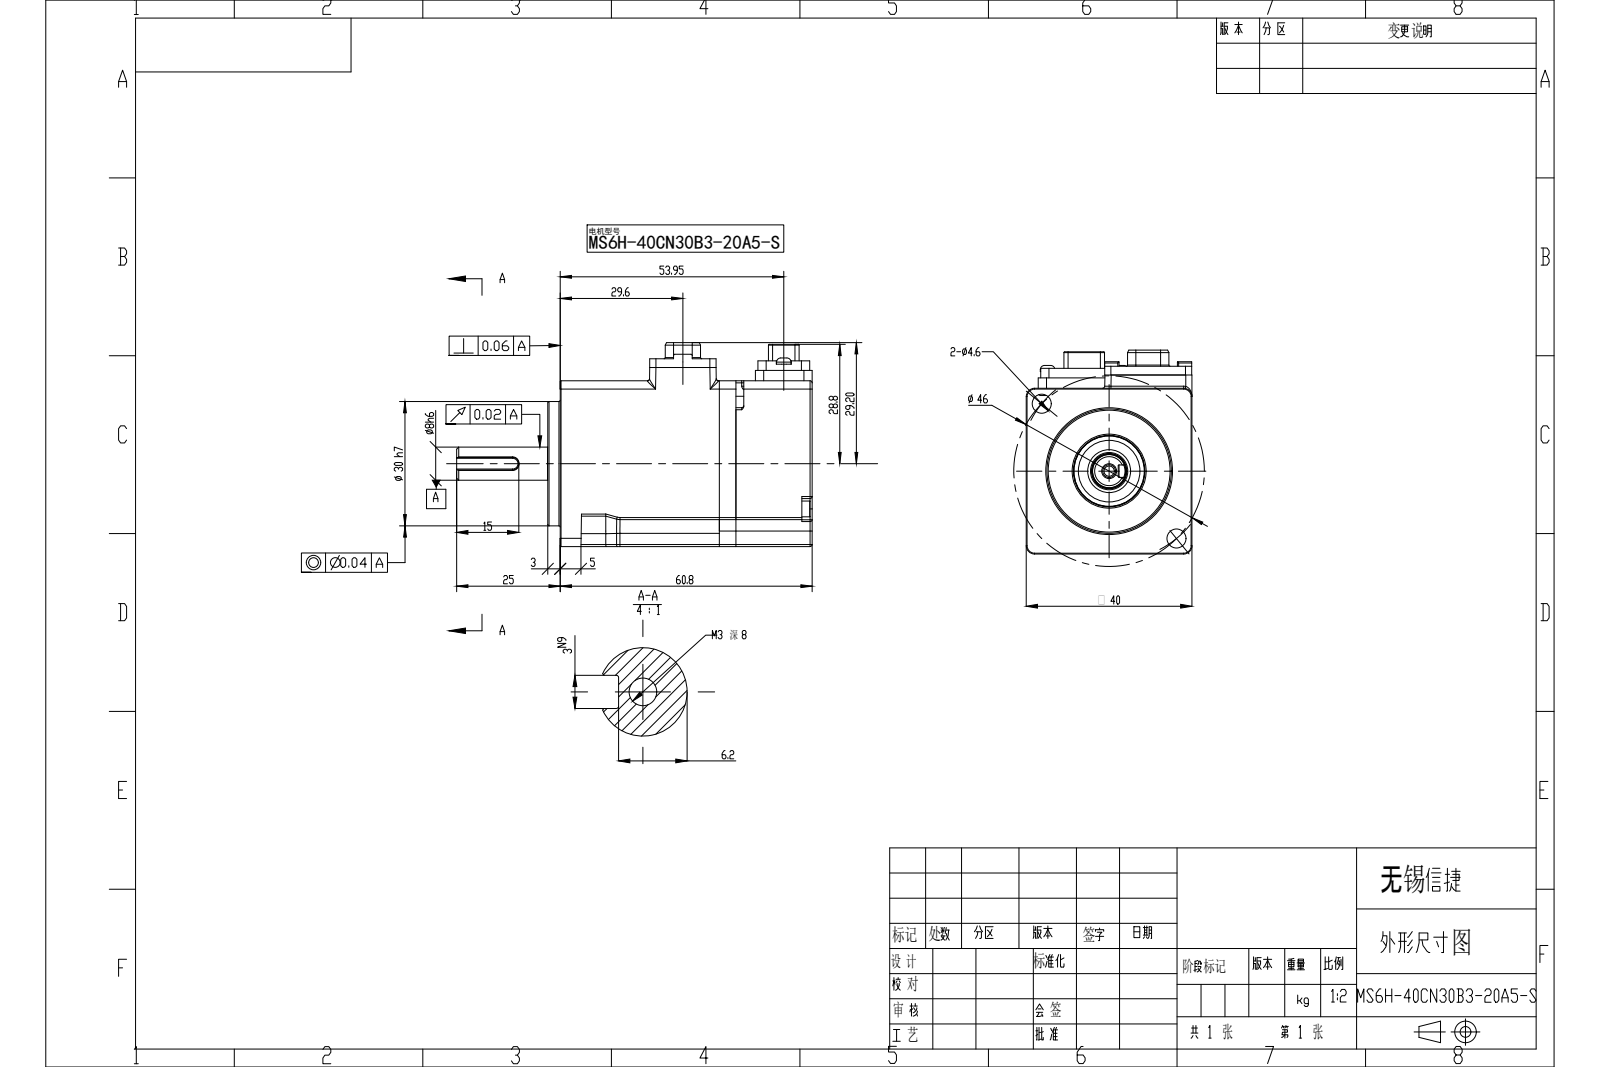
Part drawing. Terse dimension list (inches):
name: MS6H-40CN30B3-20A5-S
written by: SolidWorks 2022 (AUTOMOTIVE_DESIGN)
unit: in
bodies: 0 solids, 657 faces (334 planar, 210 cylindrical, 113 other)
size: 3.378 × 1.937 × 1.575
holes: 8× ⌀0.083, 2× ⌀0.063, 2× ⌀0.181, 1× ⌀0.098, 1× ⌀0.354, 1× ⌀0.585
bosses: 4× ⌀0.15, 2× ⌀0.138, 1× ⌀1.181, 1× ⌀0.669, 1× ⌀0.407, 1× ⌀0.335, 1× ⌀0.315
rounds: 63× R0.02, 18× R0.008, 16× R0.079, 10× R0.012, 9× R0.059, 4× R0.039, 4× R0.098, 4× R0.109
face distances: 1.575, 2.394, 0.882, 1.512, 0.157, 0.256, 1.319, 1.63, 0.118, 0.724
hole spacings: 0.23, 0.708, 0.669, 0.315, 0.461, 0.654, 0.726, 0.813
